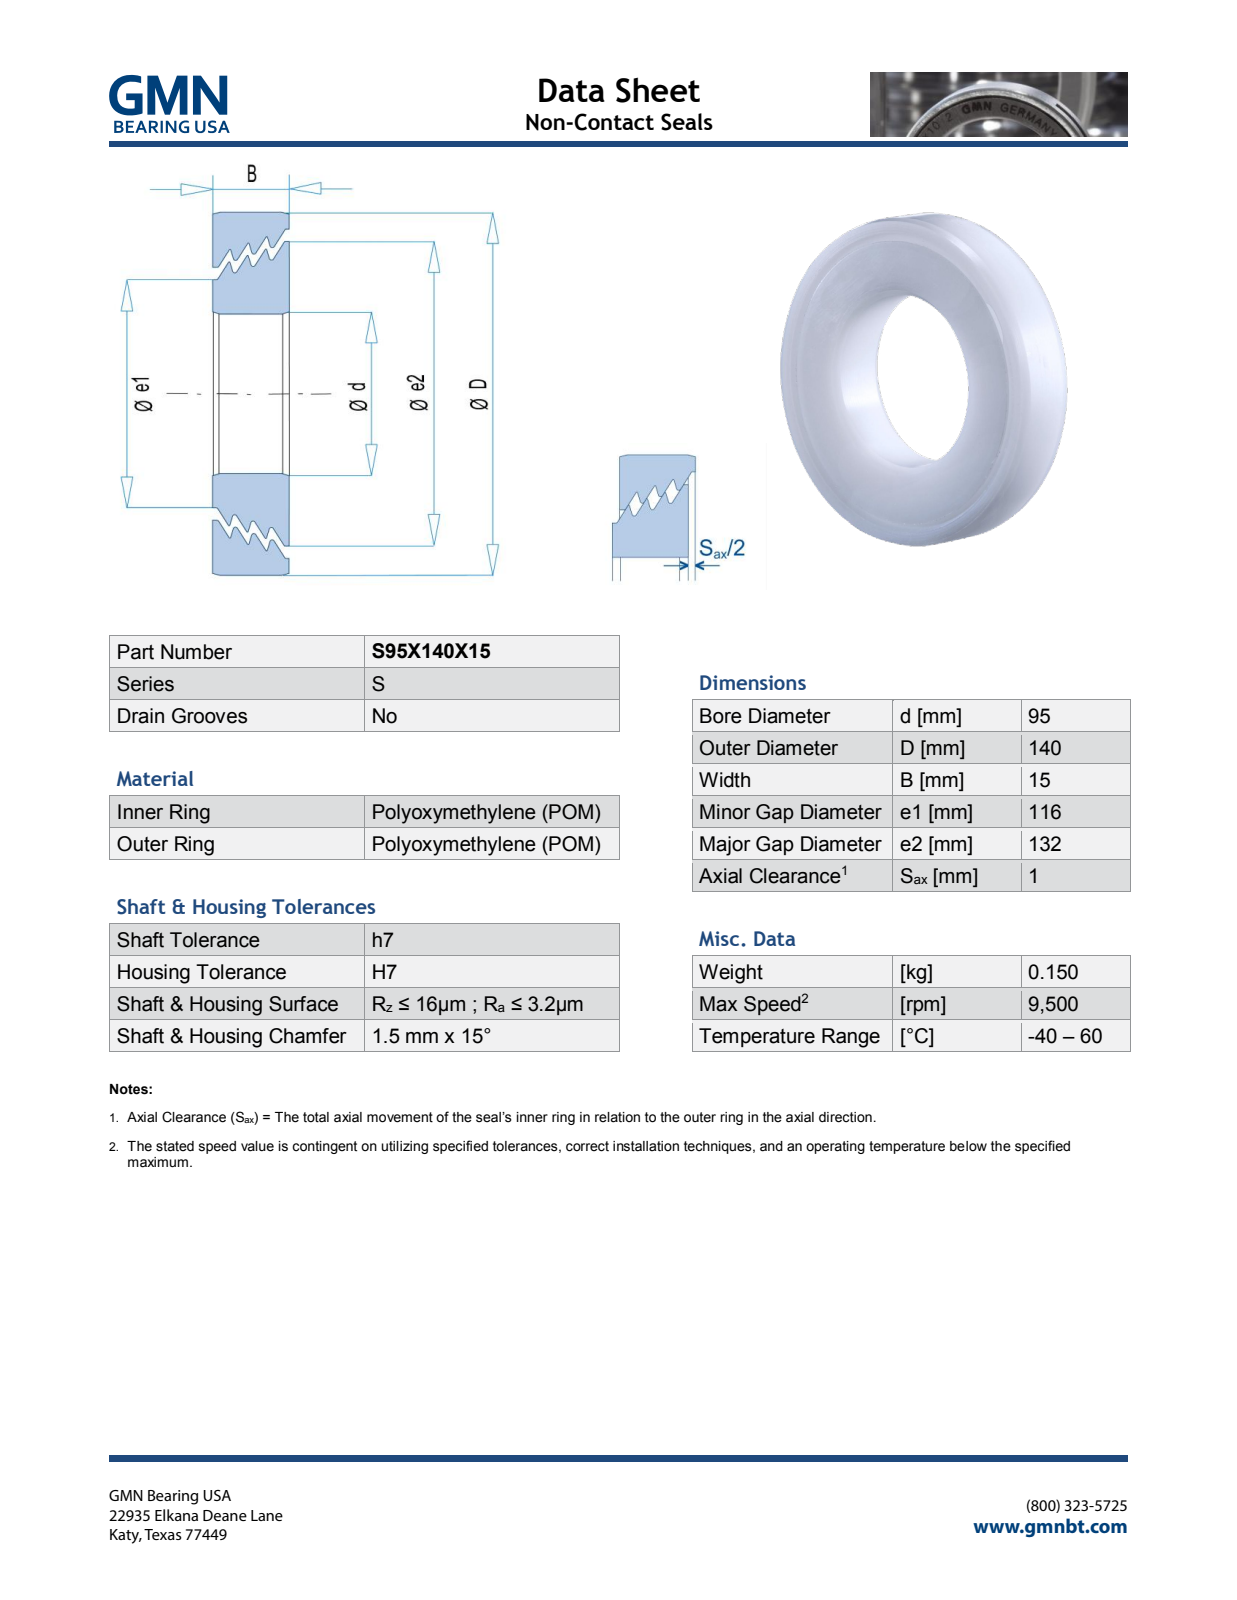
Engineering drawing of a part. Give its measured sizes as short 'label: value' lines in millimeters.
name: S95X140X15_PRT
written by: PRO/ENGINEER BY PARAMETRIC TECHNOLOGY CORPORATION, 2013150 (AUTOMOTIVE_DESIGN)
unit: mm
bodies: 2 solids, 677 faces (581 planar, 12 cylindrical, 84 other)
size: 140 × 140 × 15.07
volume: 118 089 mm³; area: 47 879 mm²
holes: 1× ⌀95, 1× ⌀117.63, 1× ⌀133.63
bosses: 1× ⌀140, 1× ⌀132, 1× ⌀116
face distances: 15, 15.07, 0.55, 4.39, 0.56, 3.84, 0.47, 3.12, 0.49, 4.4
